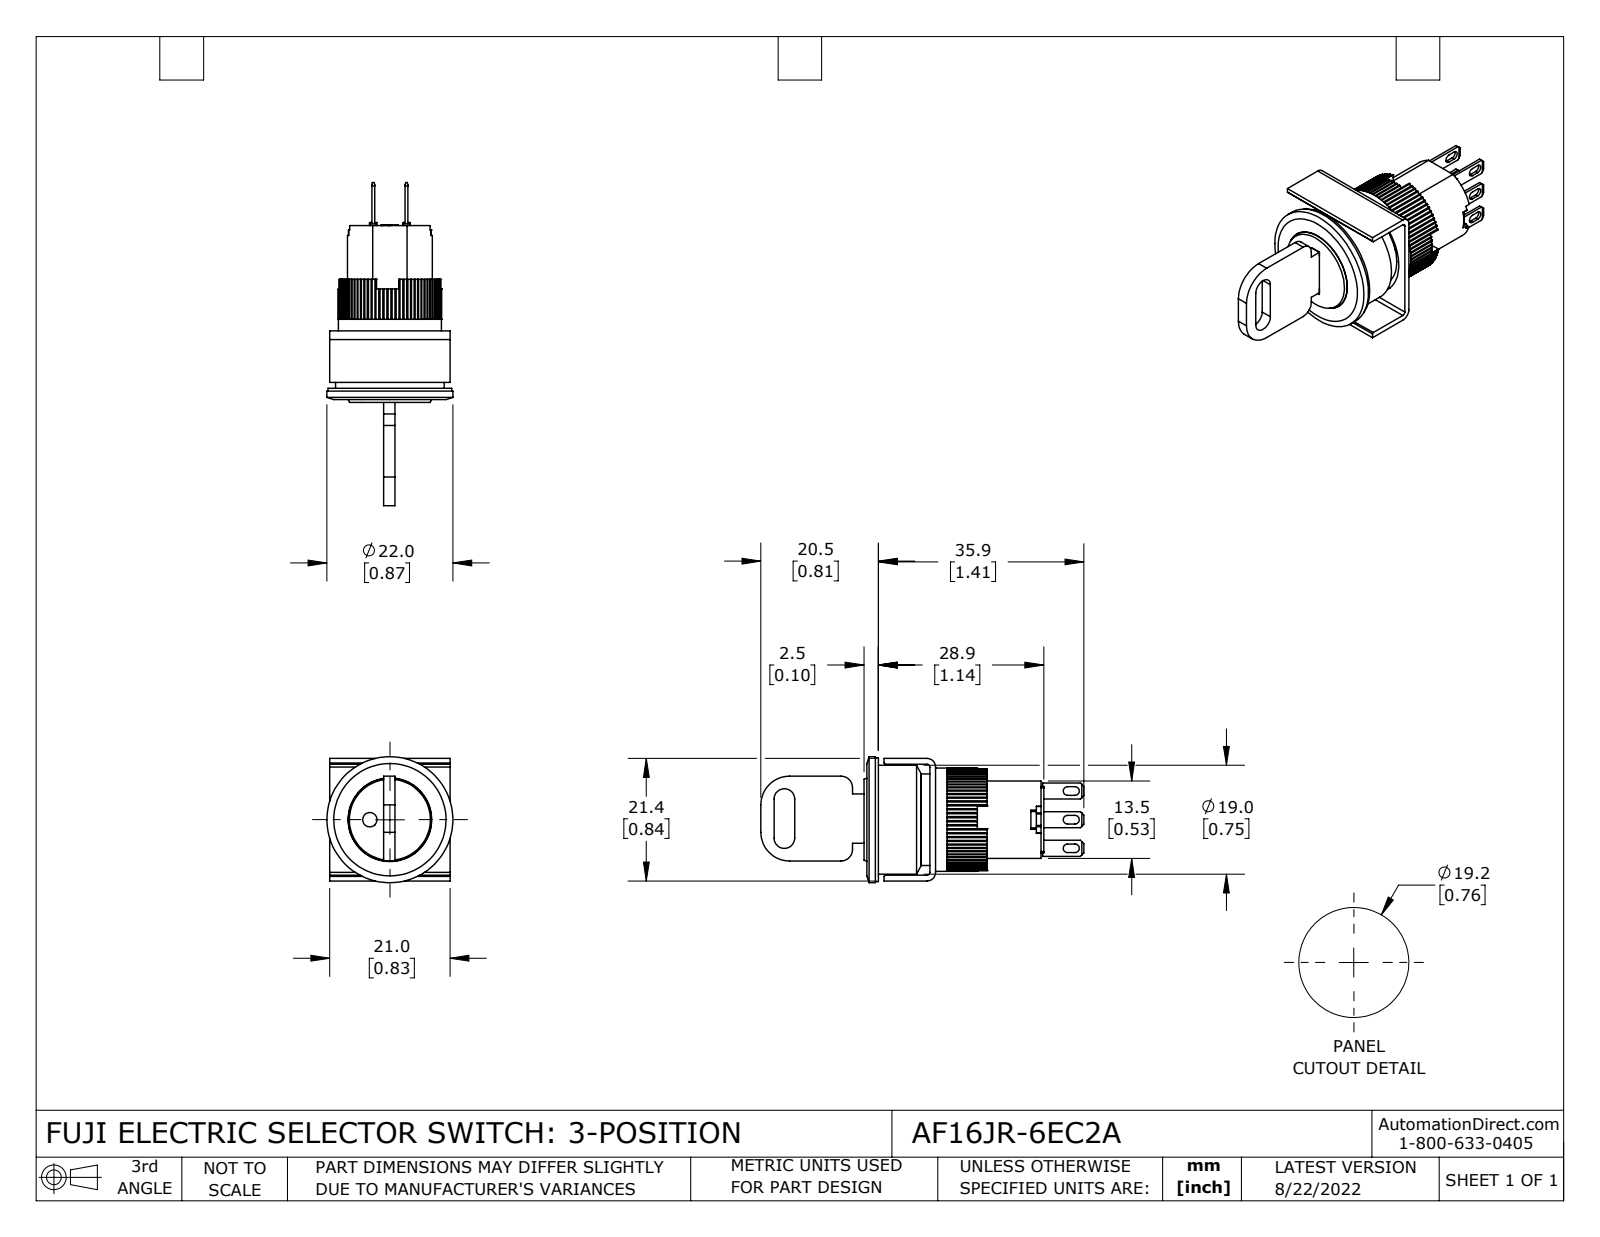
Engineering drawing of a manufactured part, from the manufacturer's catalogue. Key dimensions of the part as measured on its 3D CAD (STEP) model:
Part name (STEP PRODUCT): AF16JR-6EC2A
STEP written by: SolidWorks 2021 (CONFIG_CONTROL_DESIGN)
Units: inches
Bodies: 13 solids, 707 faces (518 planar, 183 cylindrical, 6 other)
Overall size (bounding box): 2.22 × 0.866 × 0.866
Volume: 0.495 in³ · Surface area: 11.24 in²
Round holes (diameter × count): ⌀0.039 ×1, ⌀0.098 ×1, ⌀0.575 ×1, ⌀0.709 ×1, ⌀0.748 ×1
Round bosses / shafts (diameter × count): ⌀0.866 ×1, ⌀0.85 ×1, ⌀0.63 ×1, ⌀0.583 ×1, ⌀0.571 ×1
Partial cylindrical surfaces — rounded edges, fillets, slot ends (radius × count): R0.01 ×80, R0.008 ×12, R0.03 ×6, R0.02 ×2, R0.059 ×2, R0.071 ×2, R0.079 ×2, R0.197 ×2
Main face-to-face distances: 0.079, 0.039, 0.02, 0.374, 0.177, 0.098, 0.394, 0.803, 0.059, 0.764
Hole centre spacings: 0.138
